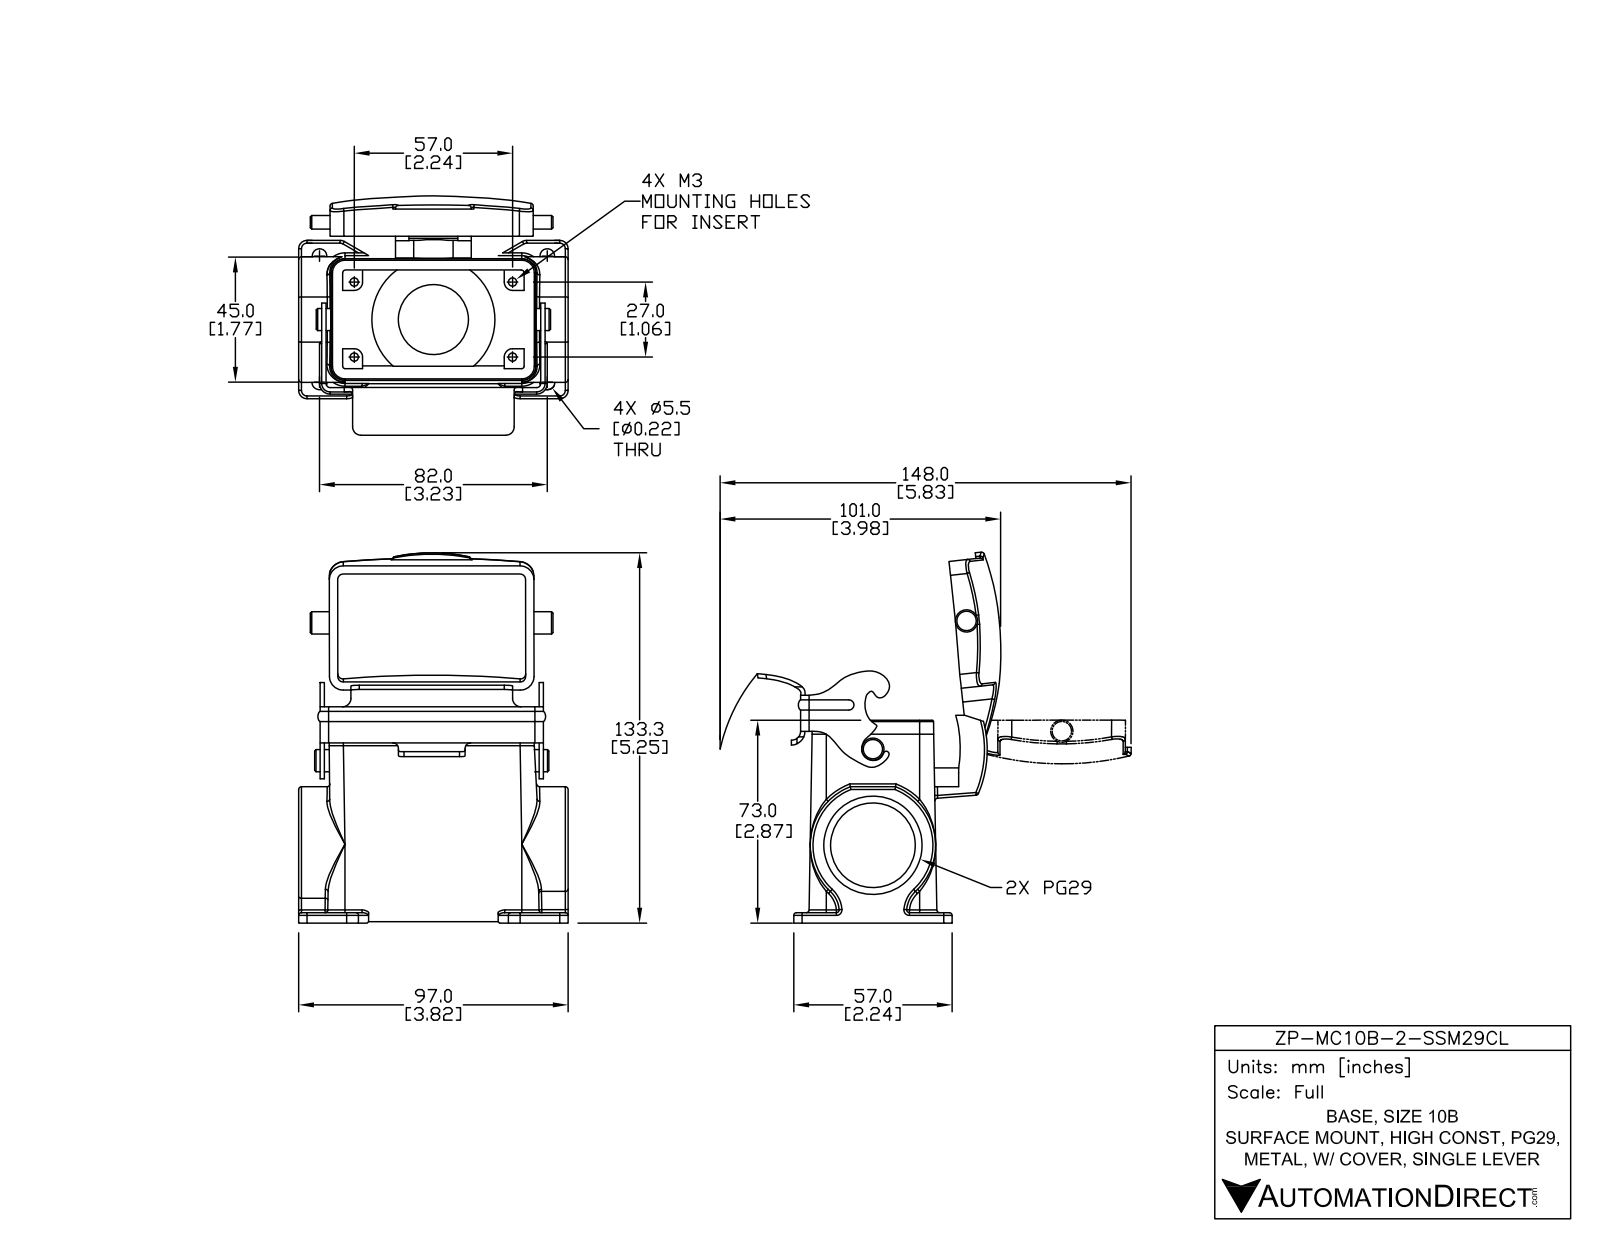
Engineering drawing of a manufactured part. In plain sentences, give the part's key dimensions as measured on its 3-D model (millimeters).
The part is named "ZP-MC10B-2-SSM29CL". Its 3-D file was written by "SolidWorks 2014 (AUTOMOTIVE_DESIGN)". It is 3 solids with 467 faces: 159 planar, 176 cylindrical and 132 other. Overall it measures 135.62 by 97 by 81.84 millimeters. Its volume is 144 250 cubic millimeters and its surface area 70 547 square millimeters. Round holes: 4 of diameter 3, 4 of diameter 5.5, 1 of diameter 2, 1 of diameter 25.23, 1 of diameter 30, 1 of diameter 35.5. Round bosses or shafts: 1 of diameter 8, 1 of diameter 7.95. Partial cylindrical surfaces (rounded edges, fillets, slot ends): 26 of radius 1, 12 of radius 3, 8 of radius 2, 6 of radius 5, 4 of radius 0.5, 4 of radius 6, 2 of radius 1.5, 2 of radius 3.06. The main face-to-face distances are 39.67, 0.5, 1.56, 69.71, 3, 5.5, 5, 9.85, 87.15, 40.49. The hole center spacings are 15.4, 31.54, 38.11, 46.77, 70.08, 78.27, 27, 45.
